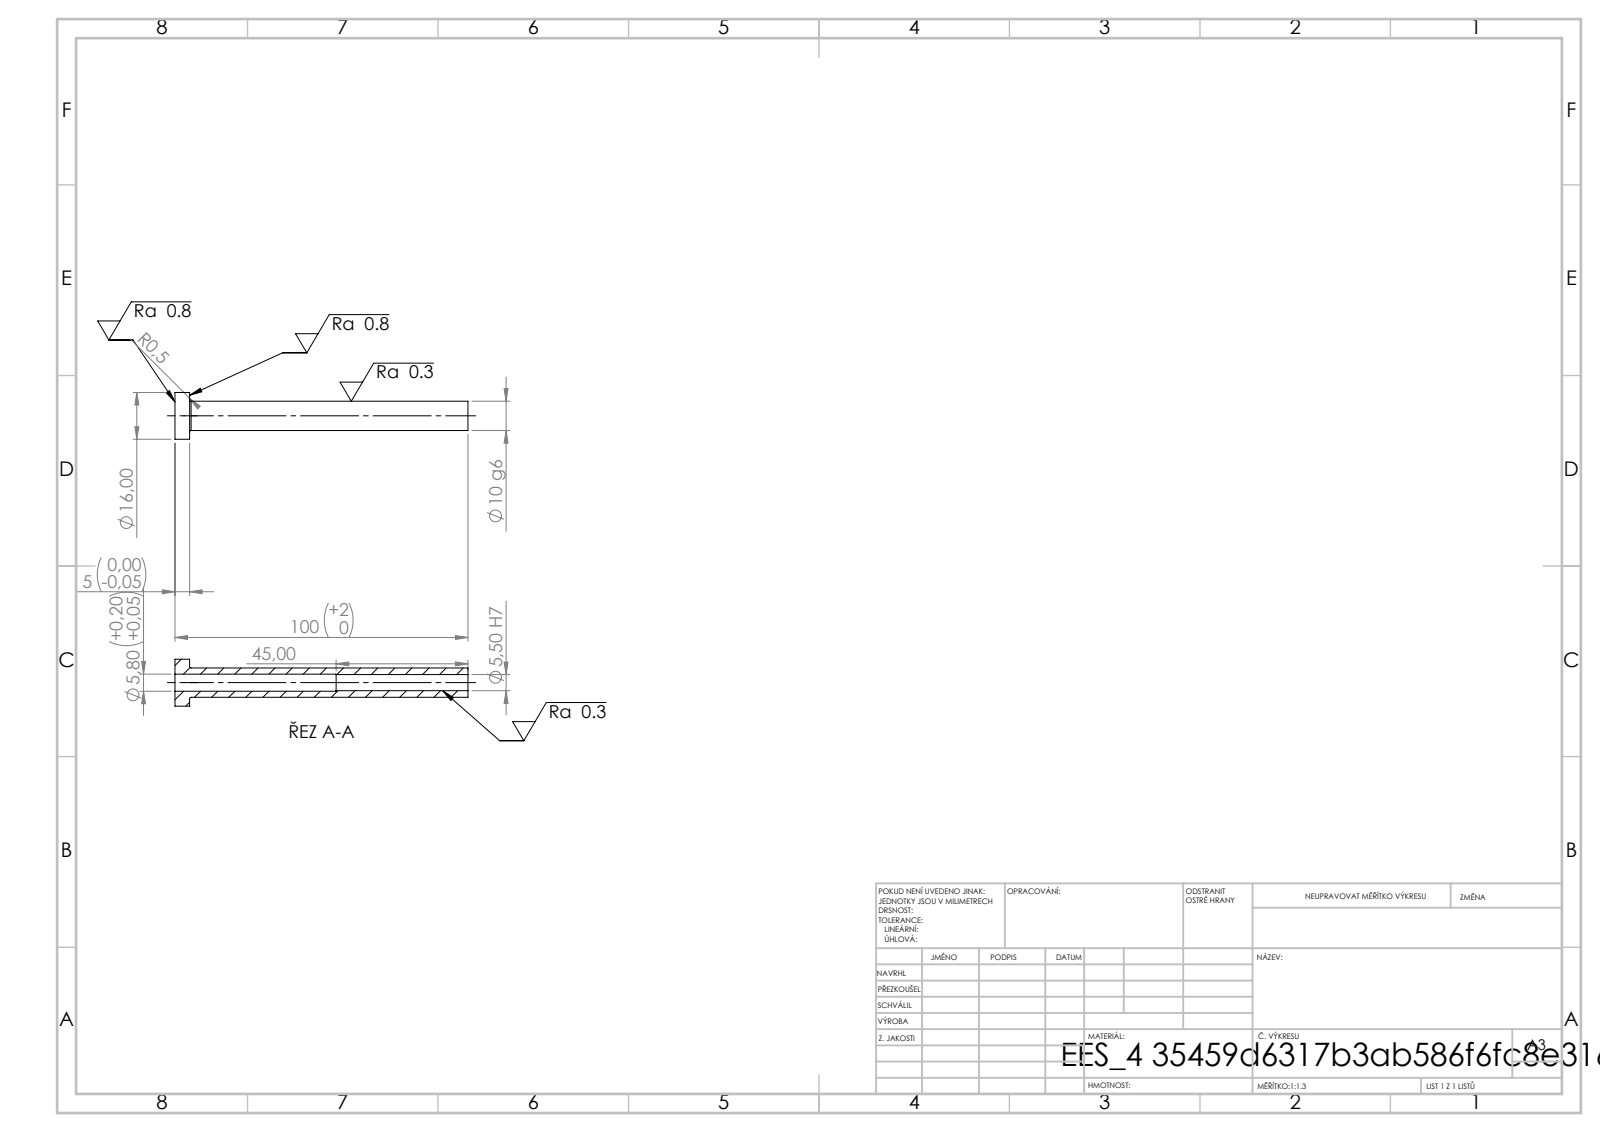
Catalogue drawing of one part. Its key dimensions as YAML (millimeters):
step_written_by: "SolidWorks 2019 (CONFIG_CONTROL_DESIGN)"
units: millimeters
bodies: {solids: 1, faces: 14, planar: 4, cylindrical: 8, other: 2}
overall_size: [100, 16, 16]
volume: 5946
surface_area: 5364
round_holes:
  - {diameter: 5.5, count: 1}
  - {diameter: 5.8, count: 1}
round_bosses_or_shafts:
  - {diameter: 16, count: 1}
  - {diameter: 10, count: 1}
face_to_face_distances: [5, 100, 95, 55, 50, 45]
